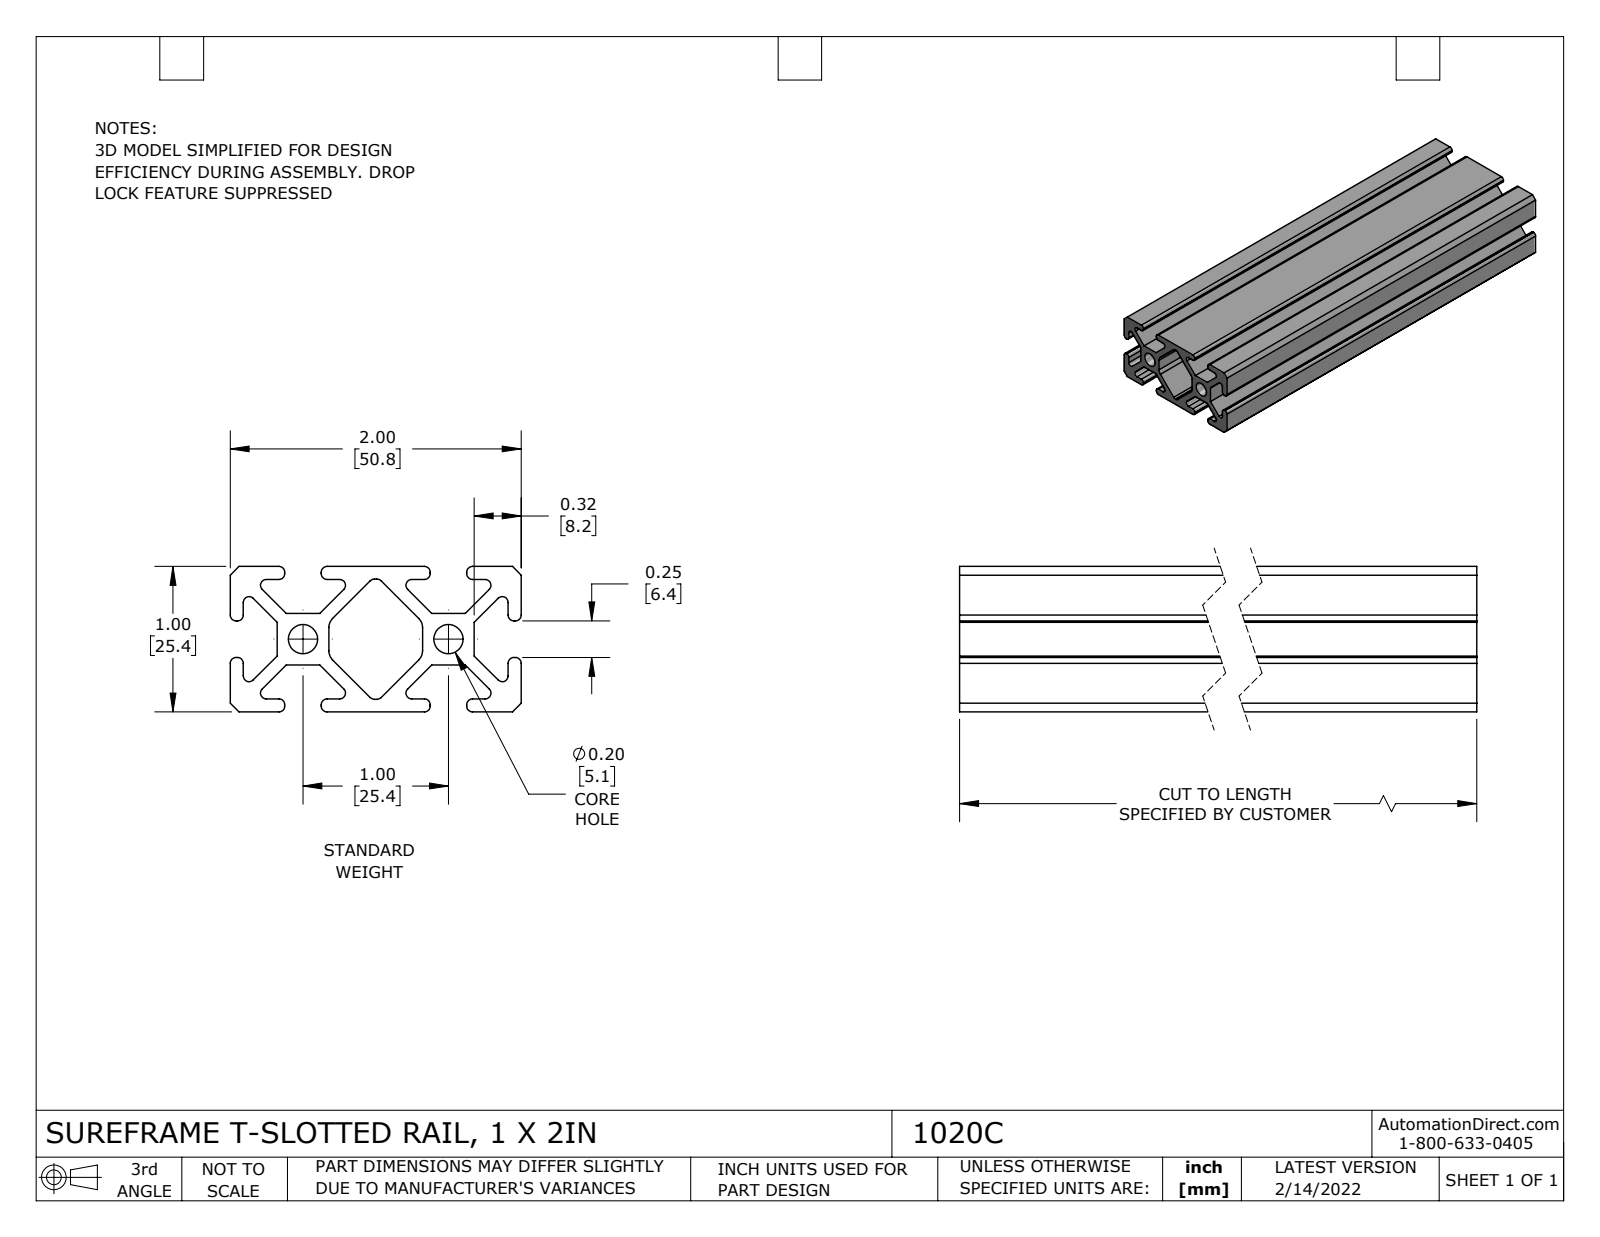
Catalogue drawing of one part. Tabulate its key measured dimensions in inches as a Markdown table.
| quantity | value |
| --- | --- |
| part name | 1020C |
| STEP written by | SolidWorks 2021 (CONFIG_CONTROL_DESIGN) |
| units | inches |
| bodies | 1 solid, 120 faces (66 planar, 54 cylindrical, 0 other) |
| overall size | 6 × 2 × 1 |
| volume | 4.825 in³ |
| surface area | 93.66 in² |
| round holes (diameter × count) | 0.201 × 2 |
| partial cylindrical surfaces (radius × count) | 0.04 × 36, 0.044 × 4, 0.087 × 4 |
| main face-to-face distances | 0.087, 0.707, 0.323, 1, 0.62, 0.09, 0.233, 0.794, 0.677, 0.91 |
| hole center spacings | 1 |
